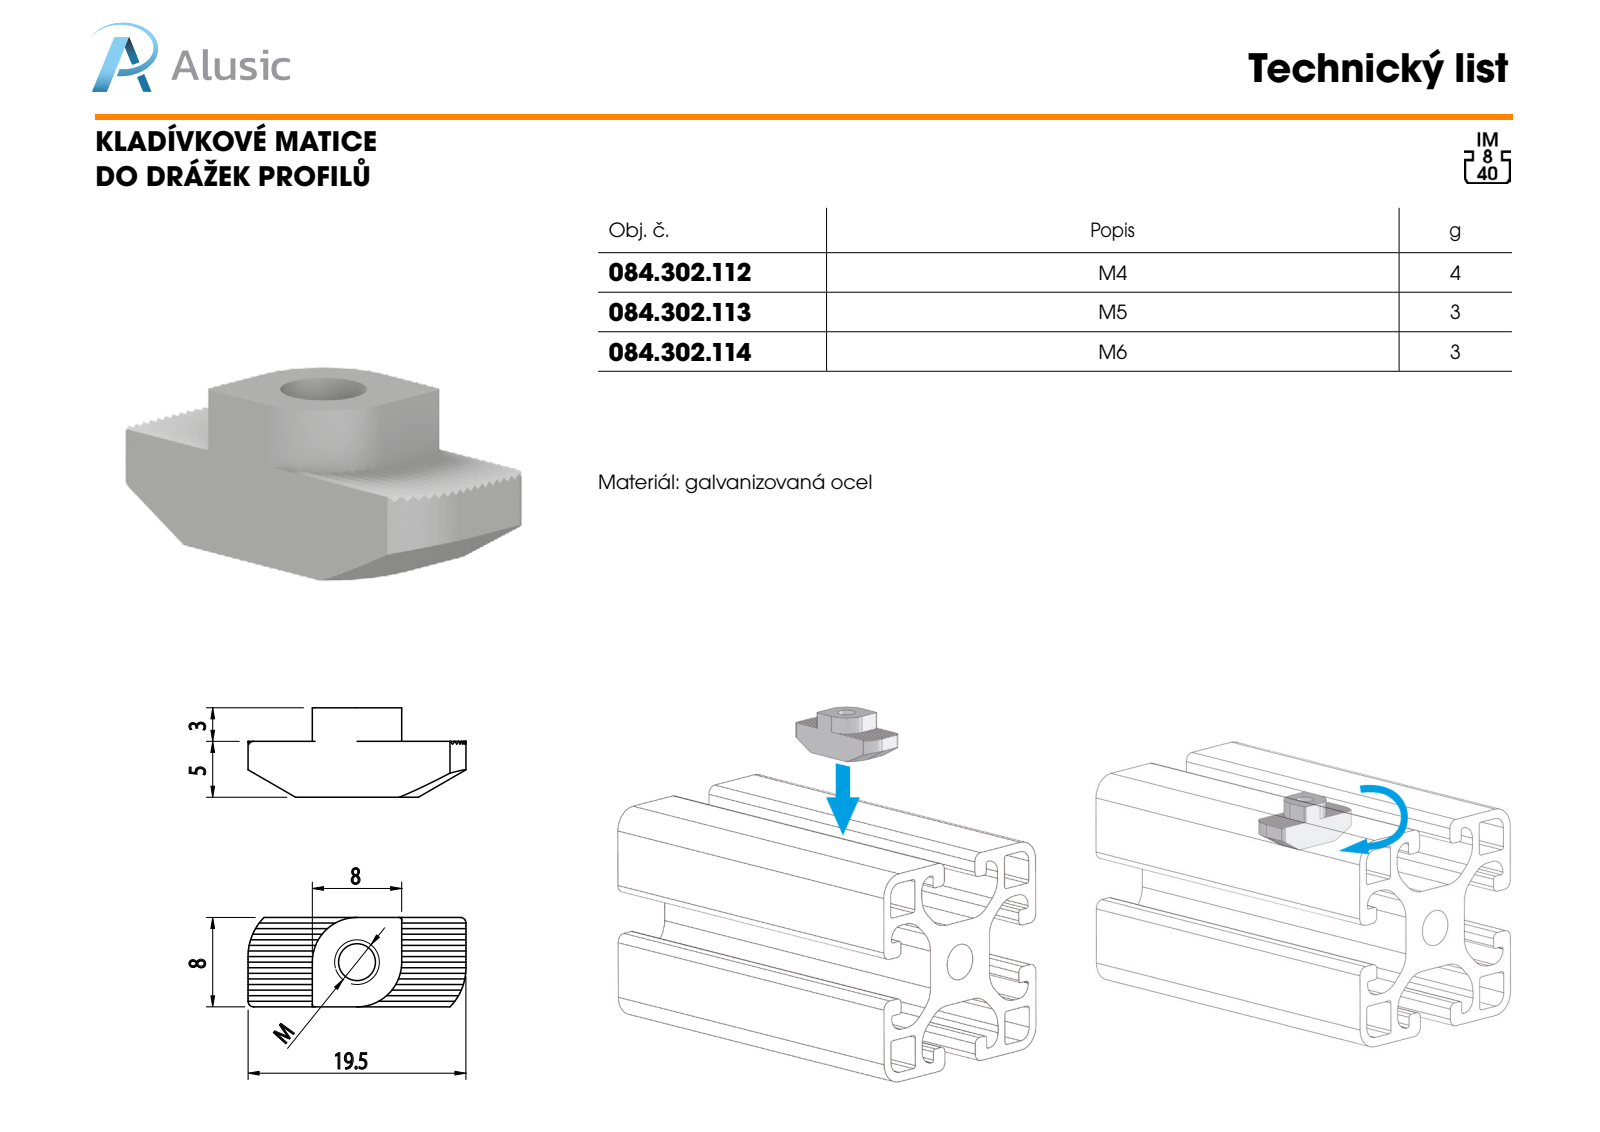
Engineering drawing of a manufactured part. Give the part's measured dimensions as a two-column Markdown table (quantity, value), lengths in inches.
| quantity | value |
| --- | --- |
| part name | 084.302.113 |
| STEP written by | SolidWorks 2016 (CONFIG_CONTROL_DESIGN) |
| units | inches |
| bodies | 1 solid, 113 faces (104 planar, 9 cylindrical, 0 other) |
| overall size | 0.768 × 0.315 × 0.315 |
| volume | 0.046 in³ |
| surface area | 1.14 in² |
| round holes (diameter × count) | 0.165 × 1 |
| partial cylindrical surfaces (radius × count) | 0.02 × 2, 0.197 × 2, 0.157 × 1 |
| main face-to-face distances | 0.315, 0.028, 0.014, 0.07, 0.014, 0.042, 0.042, 0.098, 0.056, 0.112 |
